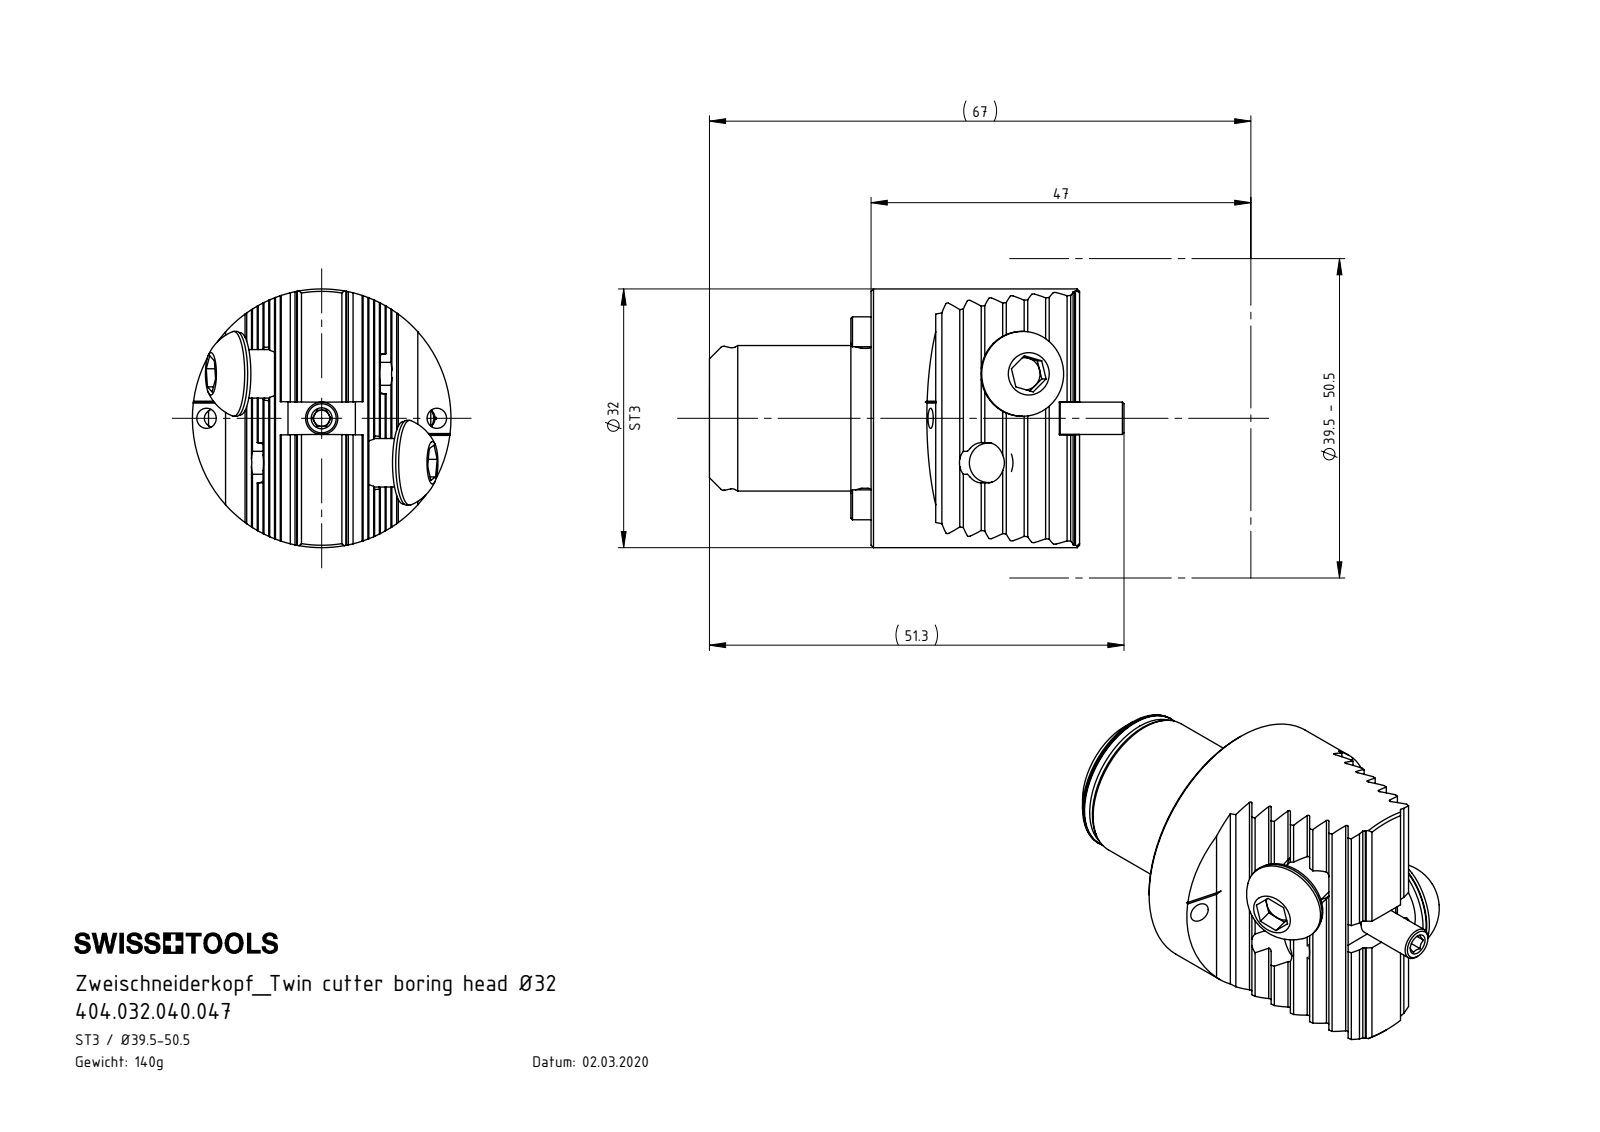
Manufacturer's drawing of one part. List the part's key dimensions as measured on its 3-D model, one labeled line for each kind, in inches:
Part name (STEP PRODUCT): ST3-Z32.K23.047_B; Z20-ER2.001.013_A; ST3.Z32.K23.047; Z32-ER1.001.016 (+3 more)
STEP written by: SolidWorks 2017 (AUTOMOTIVE_DESIGN)
Units: inches
Bodies: 8 solids, 285 faces (151 planar, 74 cylindrical, 60 other)
Overall size (bounding box): 2.02 × 1.26 × 1.26
Volume: 1.087 in³ · Surface area: 12.96 in²
Round holes (diameter × count): ⌀0.098 ×4, ⌀0.268 ×3, ⌀0.11 ×2, ⌀0.197 ×2, ⌀0.252 ×2, ⌀0.079 ×1, ⌀0.13 ×1
Round bosses / shafts (diameter × count): ⌀0.413 ×2, ⌀0.402 ×2, ⌀0.236 ×2, ⌀1.26 ×1, ⌀0.709 ×1, ⌀0.701 ×1, ⌀0.681 ×1, ⌀0.157 ×1
Partial cylindrical surfaces — rounded edges, fillets, slot ends (radius × count): R0.008 ×14, R0.02 ×4, R0.107 ×2, R0.356 ×2, R8.661 ×2
Main face-to-face distances: 0.094, 0.187, 0.281, 0.375, 0.094, 0.469, 1.016, 0.375, 0.188, 0.281
Hole centre spacings: 0.427, 0.396, 0.854
